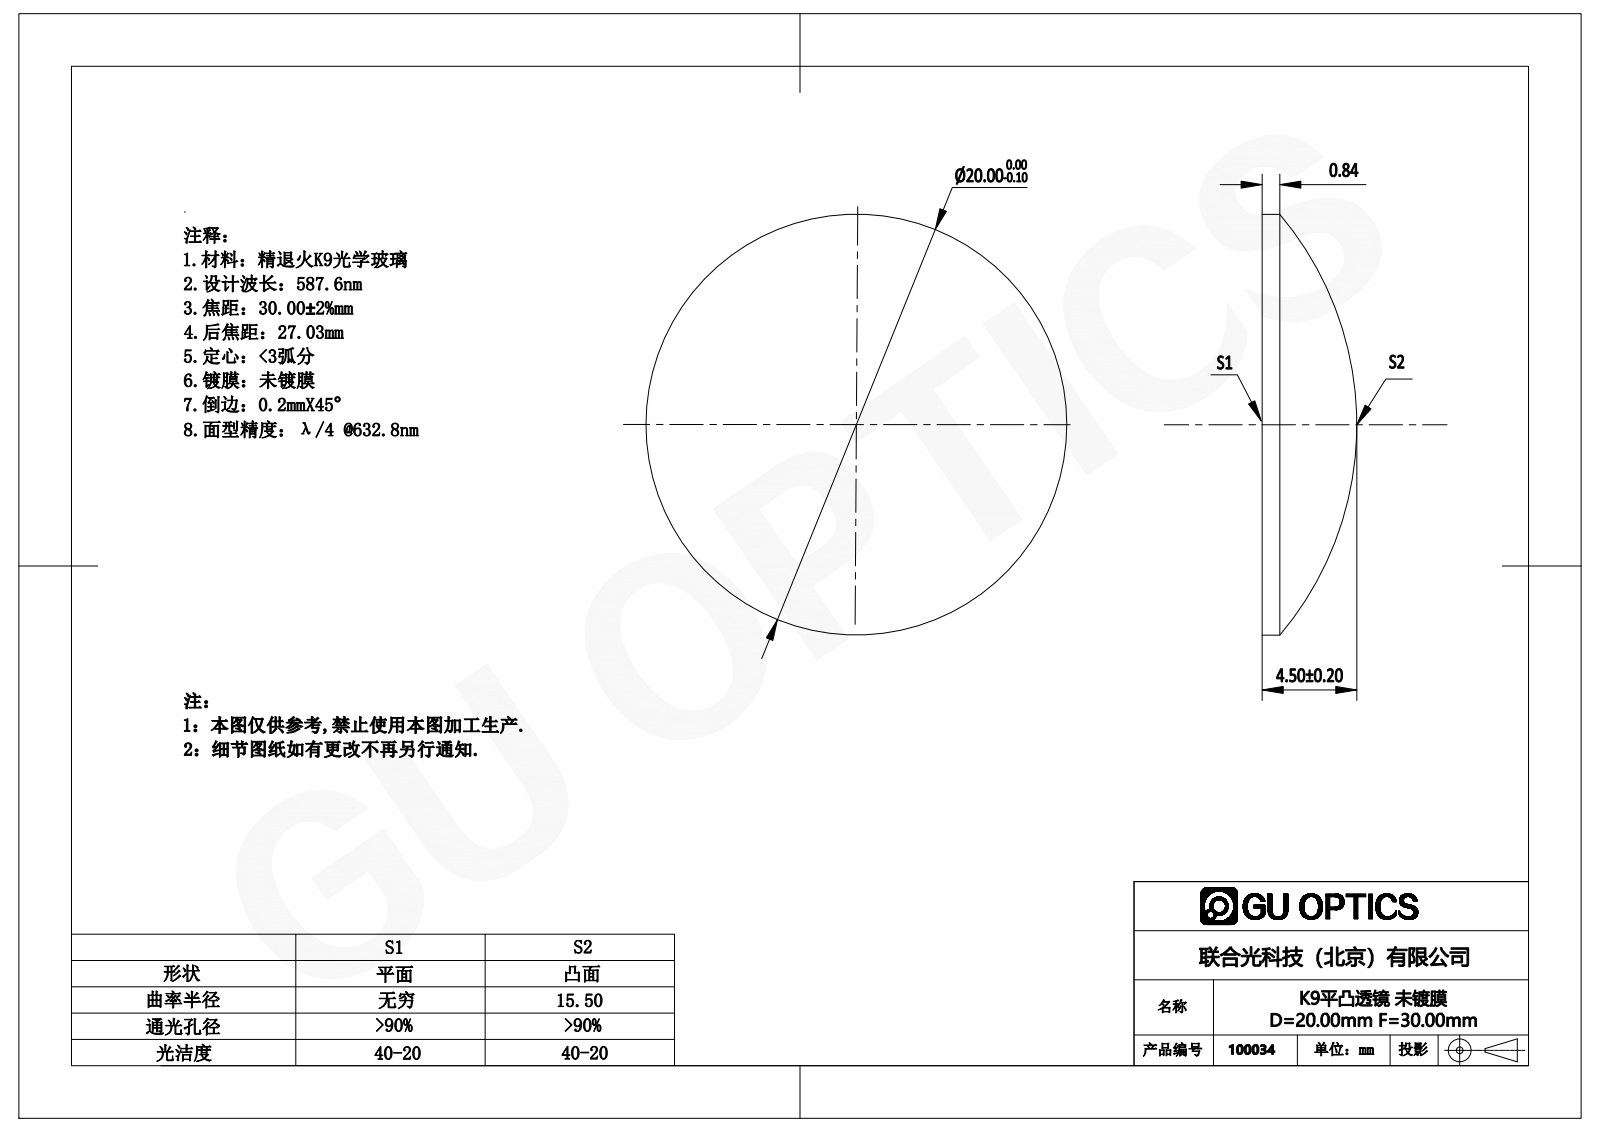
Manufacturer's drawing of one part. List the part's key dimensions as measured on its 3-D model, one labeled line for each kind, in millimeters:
Part name (STEP PRODUCT): 100034
STEP written by: SolidWorks 2016 (AUTOMOTIVE_DESIGN)
Units: millimetres
Bodies: 1 solid, 5 faces (1 planar, 2 cylindrical, 2 other)
Overall size (bounding box): 20 × 20 × 4.5
Volume: 864 mm³ · Surface area: 723 mm²
Round bosses / shafts (diameter × count): ⌀20 ×1
